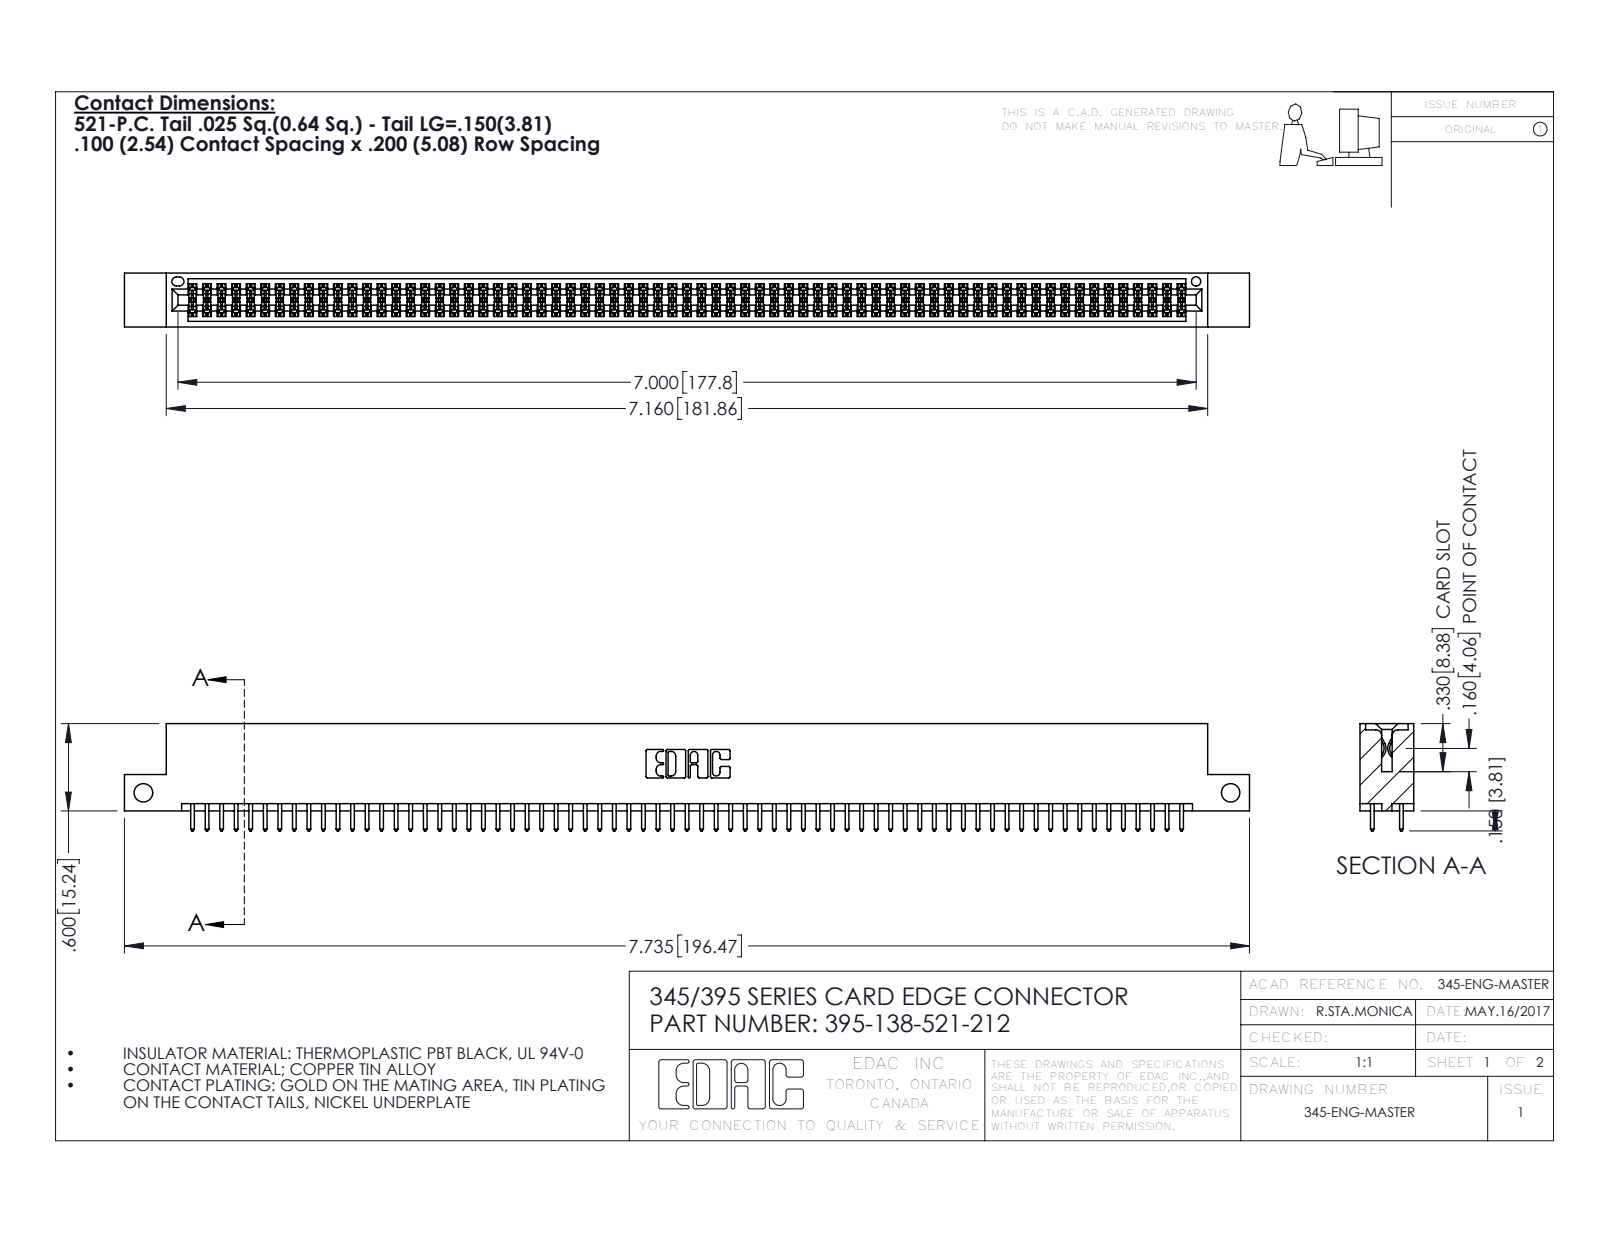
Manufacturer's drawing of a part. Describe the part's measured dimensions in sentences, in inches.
The part is named "345-292-001_345-293-121; 345 Part_Flush Mounting Lugs - Side Mount; 395-138-521-212". Its 3-D file was written by "SolidWorks 2016 (CONFIG_CONTROL_DESIGN)". It is 139 solids with 7026 faces: 4634 planar, 2392 cylindrical and 0 other. Overall it measures 7.735 by 0.737 by 0.37 inches. Its volume is 1.171 cubic inches and its surface area 44 square inches. Round holes: 2 of diameter 0.128, 1 of diameter 0.064. Partial cylindrical surfaces (rounded edges, fillets, slot ends): 207 of radius 0.006, 138 of radius 0.01, 22 of radius 0.01, 6 of radius 0.007, 6 of radius 0.031, 3 of radius 0.026, 2 of radius 0.014, 2 of radius 0.019. The main face-to-face distances are 0.298, 0.072, 0.2, 0.098, 0.272, 0.025, 0.37, 0.225, 0.175, 0.149. The hole center spacings are 7.475.
